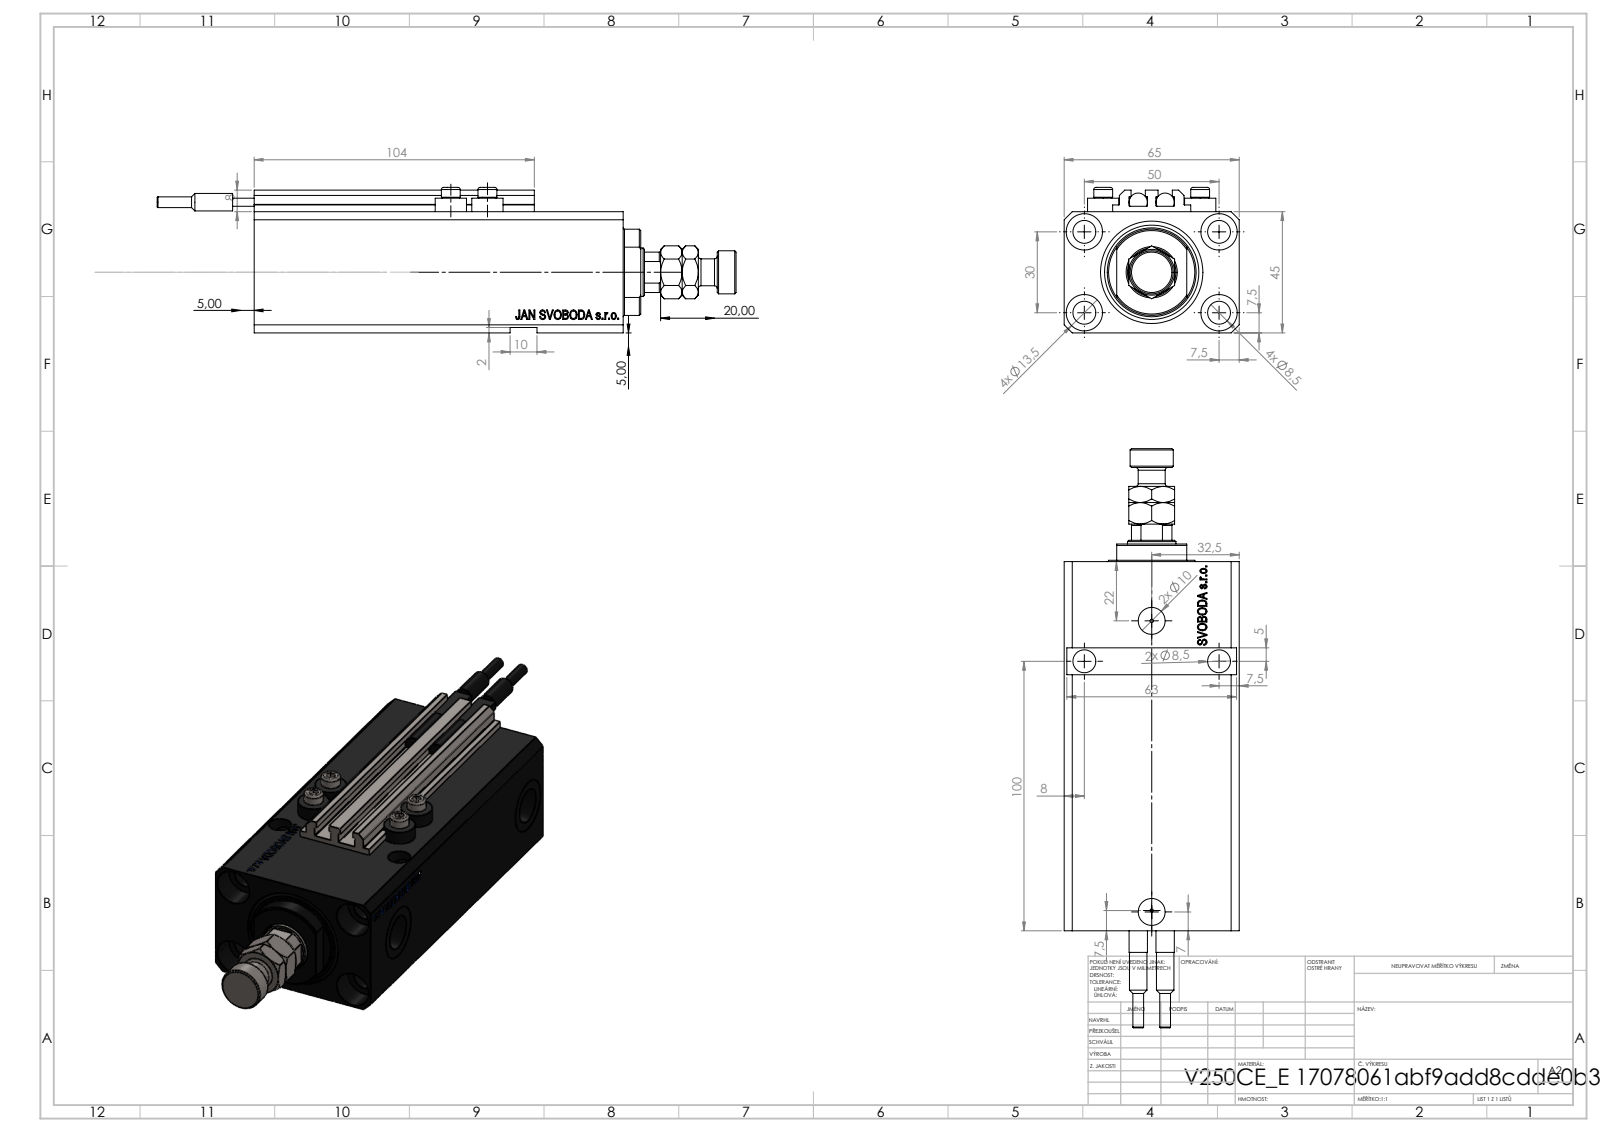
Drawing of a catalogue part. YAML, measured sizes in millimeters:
part_name: "MFA; SWITCH_V250CE; V250CE_E_Body; V250CE_VC_E (+2 more)"
step_written_by: "SolidWorks 2019 (CONFIG_CONTROL_DESIGN)"
units: millimeters
bodies: {solids: 11, faces: 1191, planar: 559, cylindrical: 162, other: 470}
overall_size: [215, 65, 54]
volume: 359492
surface_area: 98361
round_holes:
  - {diameter: 8.5, count: 9}
  - {diameter: 1.25, count: 4}
  - {diameter: 4, count: 4}
  - {diameter: 13.5, count: 4}
  - {diameter: 10, count: 2}
  - {diameter: 13.16, count: 2}
  - {diameter: 20, count: 2}
  - {diameter: 18, count: 1}
  - {diameter: 25, count: 1}
  - {diameter: 38, count: 1}
round_bosses_or_shafts:
  - {diameter: 11.6, count: 4}
  - {diameter: 7, count: 4}
  - {diameter: 6.8, count: 2}
  - {diameter: 6.5, count: 2}
  - {diameter: 4, count: 2}
  - {diameter: 16, count: 1}
  - {diameter: 10, count: 1}
partial_cylinders:
  - {radius: 0.2, count: 10}
  - {radius: 8.5, count: 1}
  - {radius: 16, count: 1}
face_to_face_distances: [45, 65, 47, 2, 14, 2.5, 10, 3, 123, 20.5]
hole_center_spacings: [29.15, 50, 13.6, 15.12, 27.89, 30, 33.61, 33.62]
